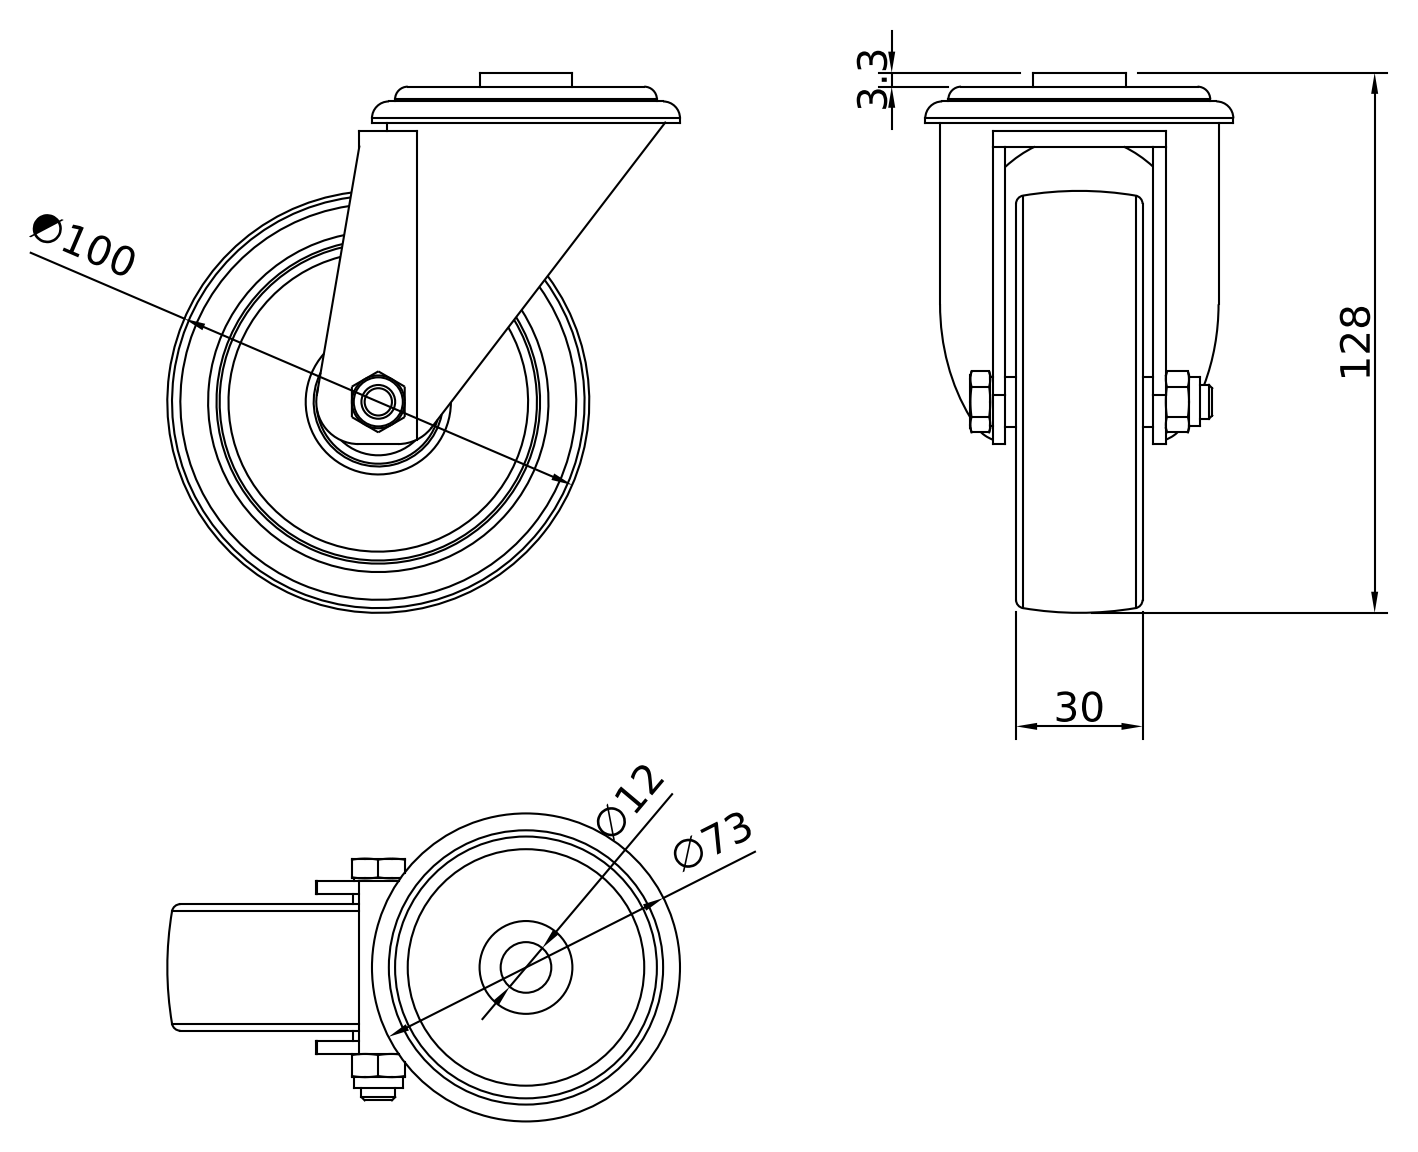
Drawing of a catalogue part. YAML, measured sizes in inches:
part_name: "CRUST0000183; 440000025926; 440000025927; 440000025925"
step_written_by: "Autodesk Inventor 2022 (AUTOMOTIVE_DESIGN)"
units: inches
bodies: {solids: 3, faces: 106, planar: 42, cylindrical: 20, other: 44}
overall_size: [5.039, 4.783, 2.874]
volume: 12.4
surface_area: 95.07
round_holes:
  - {diameter: 0.472, count: 2}
  - {diameter: 0.354, count: 1}
  - {diameter: 2.402, count: 1}
round_bosses_or_shafts:
  - {diameter: 2.874, count: 1}
  - {diameter: 2.598, count: 1}
  - {diameter: 2.443, count: 1}
  - {diameter: 0.866, count: 1}
  - {diameter: 0.458, count: 1}
  - {diameter: 0.315, count: 1}
partial_cylinders:
  - {radius: 0.394, count: 2}
face_to_face_distances: [0.098, 0.217, 0.118, 1.28, 1.398, 1.496, 0.421, 1.181, 1.378, 1.614]
